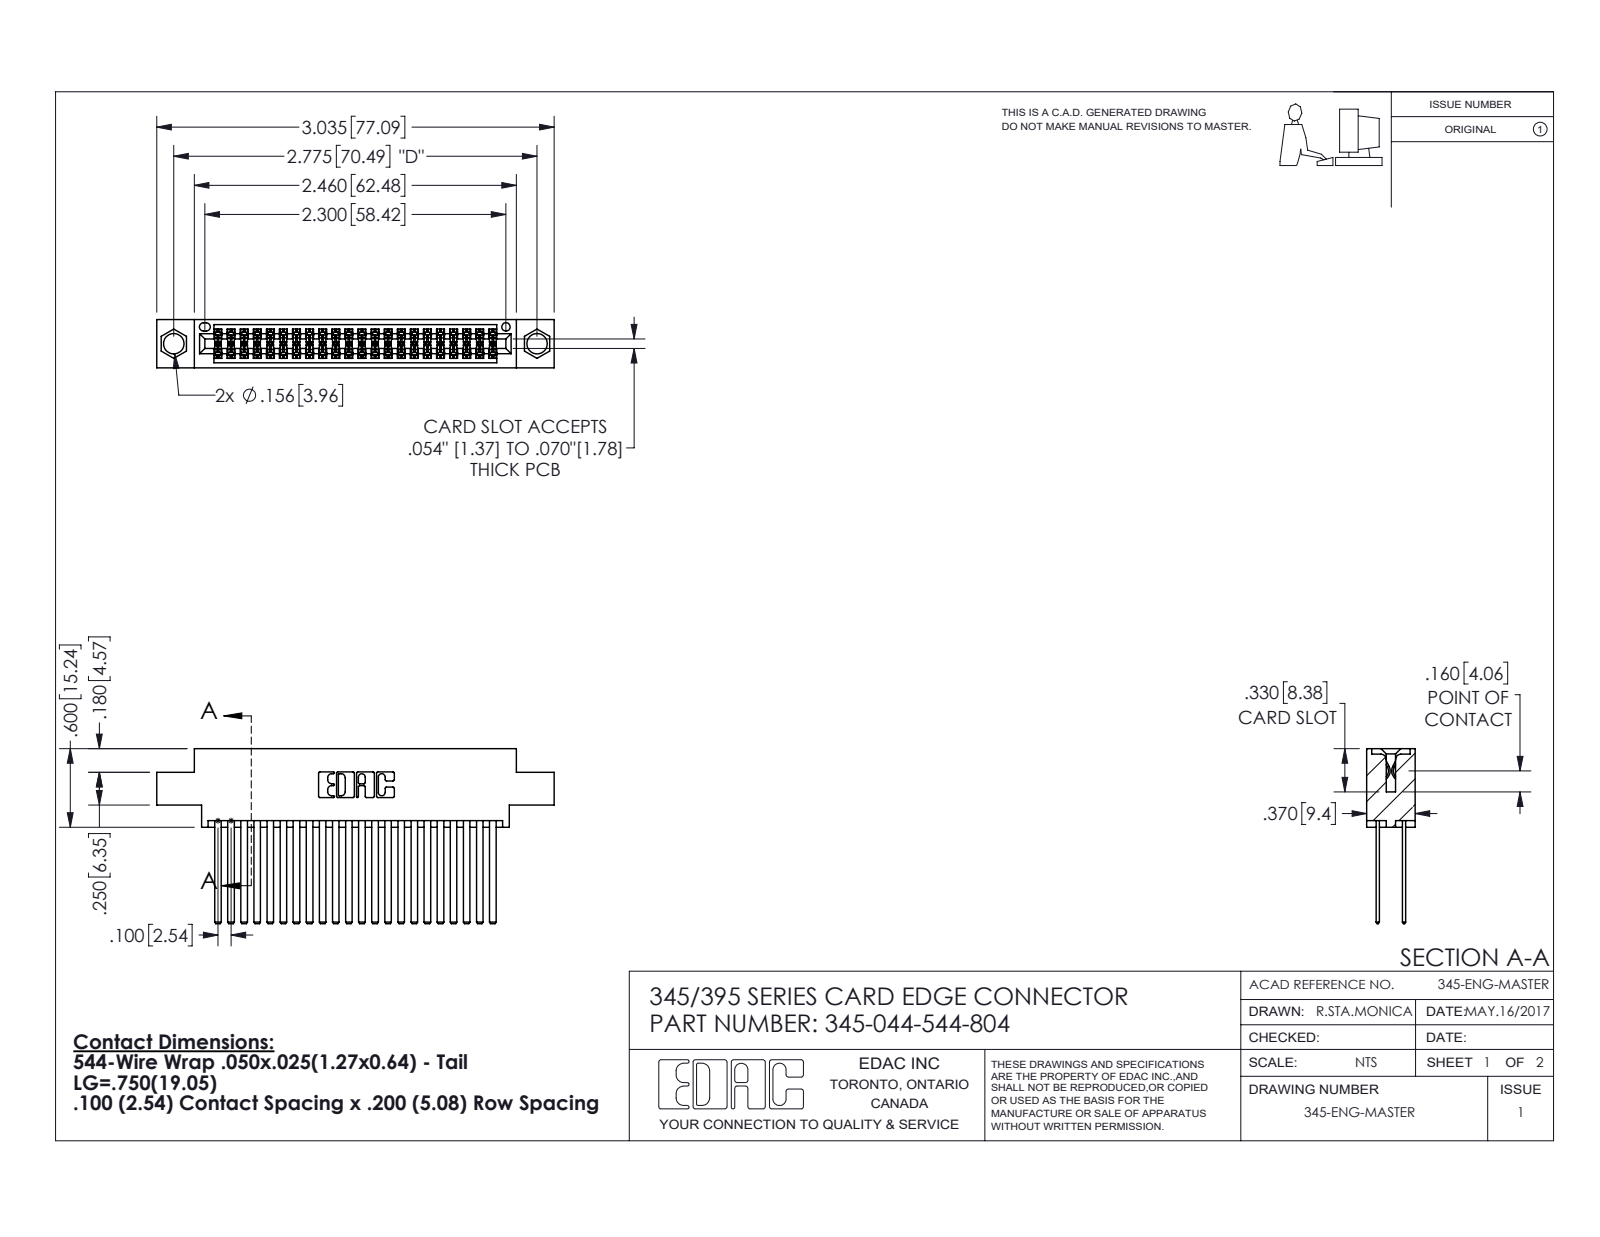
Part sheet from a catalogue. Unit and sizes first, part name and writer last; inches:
Units: inches
Overall size (bounding box): 3.035 × 1.337 × 0.37
Round holes (diameter × count): ⌀0.156 ×2, ⌀0.064 ×1
Partial cylindrical surfaces — rounded edges, fillets, slot ends (radius × count): R0.006 ×88, R0.01 ×22, R0.007 ×6, R0.031 ×6, R0.026 ×3, R0.014 ×2, R0.019 ×2, R0.022 ×2
Main face-to-face distances: 0.2, 0.072, 0.298, 0.098, 0.272, 0.025, 0.225, 0.37, 0.175, 0.15
Hole centre spacings: 0.27, 2.541, 2.775
Volume: 0.47 in³ · Surface area: 19.84 in²
Bodies: 45 solids, 2080 faces (1374 planar, 706 cylindrical, 0 other)
Part name (STEP PRODUCT): 345-044-544-804; 345-292-001_345-293-144; 345 Part_0.170 Offset - 0.156 Dia-TI
STEP written by: SolidWorks 2020 (CONFIG_CONTROL_DESIGN)
